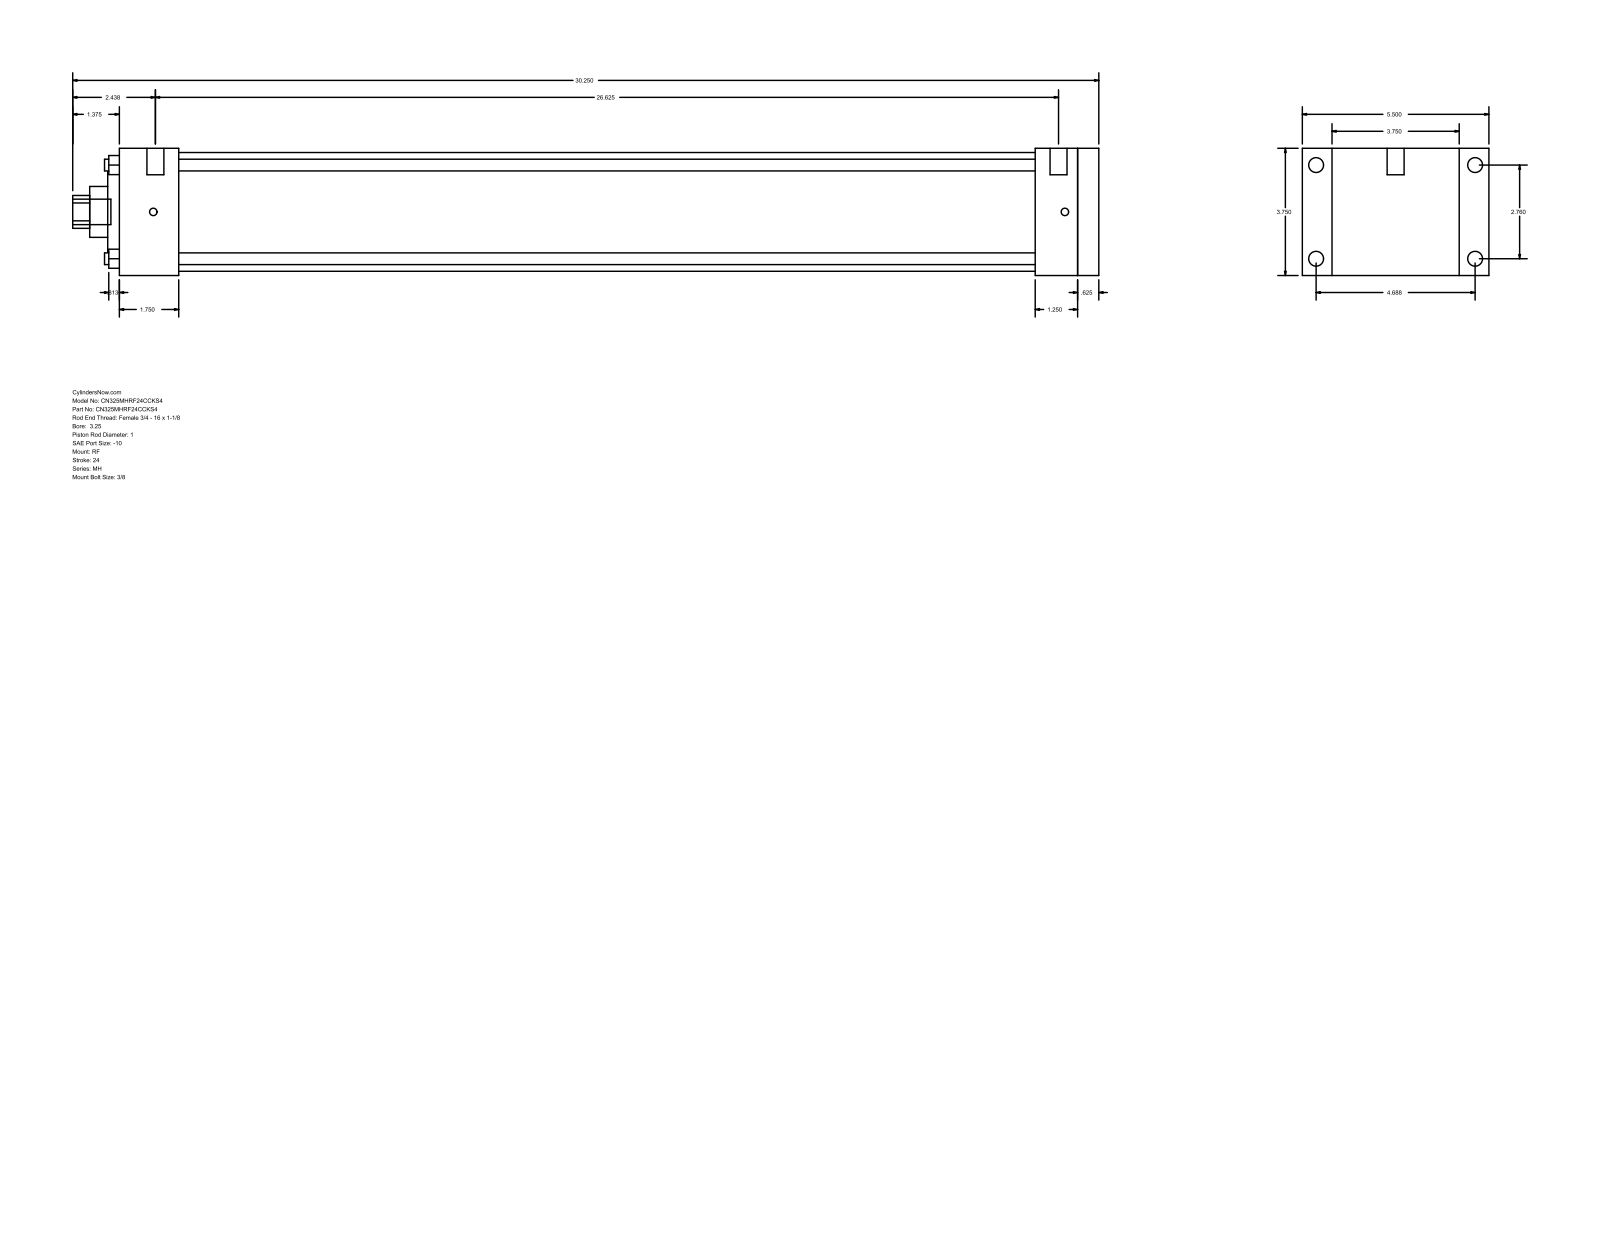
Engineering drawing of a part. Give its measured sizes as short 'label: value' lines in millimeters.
name: MH_RF__0325_1
written by: GSSL Pune (CONFIG_CONTROL_DESIGN)
unit: mm
bodies: 0 solids, 94 faces (65 planar, 29 cylindrical, 0 other)
size: 768.35 × 139.7 × 95.25
holes: 4× ⌀8.76, 1× ⌀25.4, 1× ⌀38.1, 1× ⌀60.33, 1× ⌀88.9
bosses: 4× ⌀11.13, 4× ⌀5.56, 2× ⌀12.7, 1× ⌀19.05
rounds: 1× R12.29
face distances: 95.24, 733.43, 15.87, 717.56, 22.23, 117.47, 44.46, 673.1, 688.97, 685.81
hole spacings: 49.57, 70.1, 99.14
